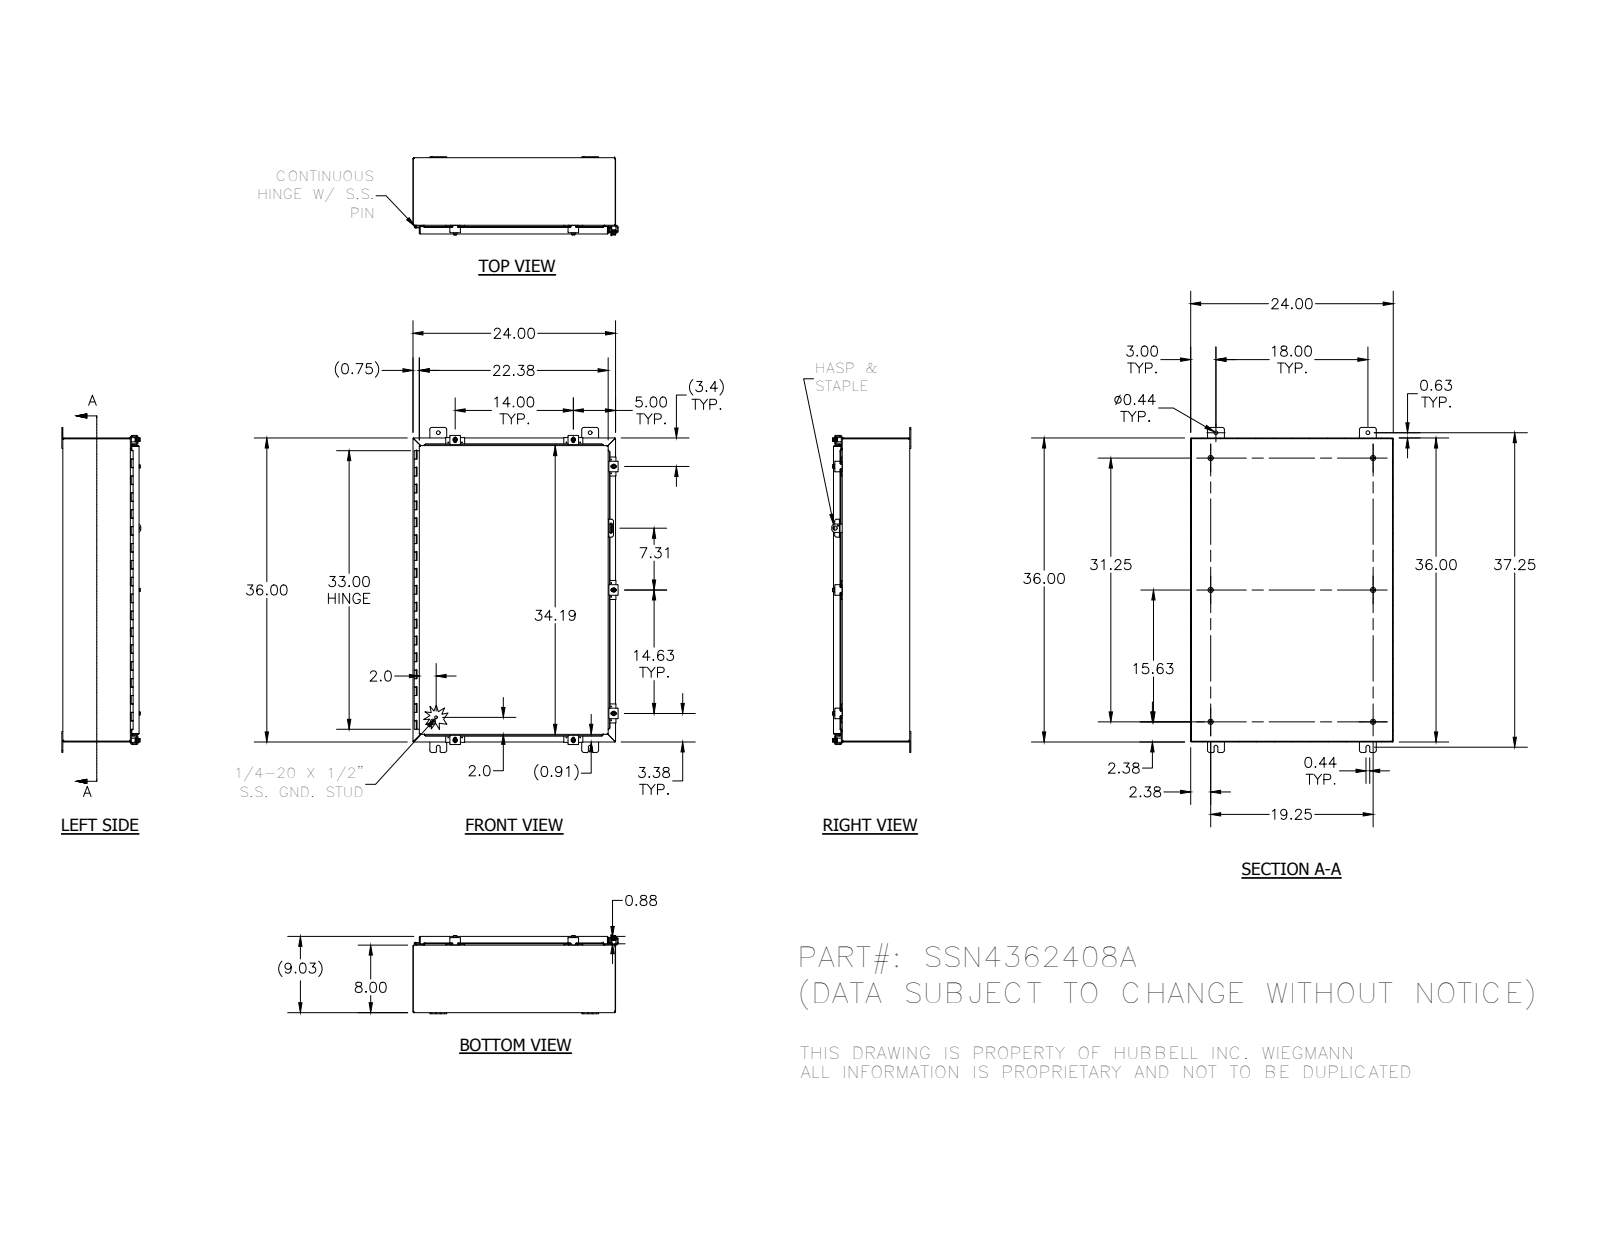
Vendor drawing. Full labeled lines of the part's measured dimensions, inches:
Part name (STEP PRODUCT): 30818; 30824-2; 30824-1; 30824-4 (+8 more)
STEP written by: SolidWorks 2014 (AUTOMOTIVE_DESIGN)
Units: inches
Bodies: 54 solids, 2180 faces (862 planar, 947 cylindrical, 371 other)
Overall size (bounding box): 38.5 × 24.216 × 9.355
Volume: 240.6 in³ · Surface area: 6 334 in²
Round holes (diameter × count): ⌀0.11 ×14, ⌀0.211 ×7, ⌀0.281 ×7, ⌀0.3 ×7, ⌀0.438 ×4, ⌀0.125 ×1, ⌀0.156 ×1, ⌀0.5 ×1
Round bosses / shafts (diameter × count): ⌀0.25 ×9, ⌀0.52 ×7, ⌀0.5 ×7, ⌀0.35 ×7, ⌀0.625 ×6, ⌀0.33 ×6, ⌀0.337 ×1, ⌀0.12 ×1
Partial cylindrical surfaces — rounded edges, fillets, slot ends (radius × count): R0.03 ×83, R0.125 ×37, R0.25 ×33, R0.031 ×23, R0.105 ×23, R0.062 ×18, R0.141 ×14, R0.1 ×10
Main face-to-face distances: 0.074, 8.959, 8.885, 9.033, 23.926, 35.926, 7.926, 1.033, 23.852, 24
Hole centre spacings: 0.876, 35.298, 14, 1.625, 13.191, 14.816, 34.961, 34.998
